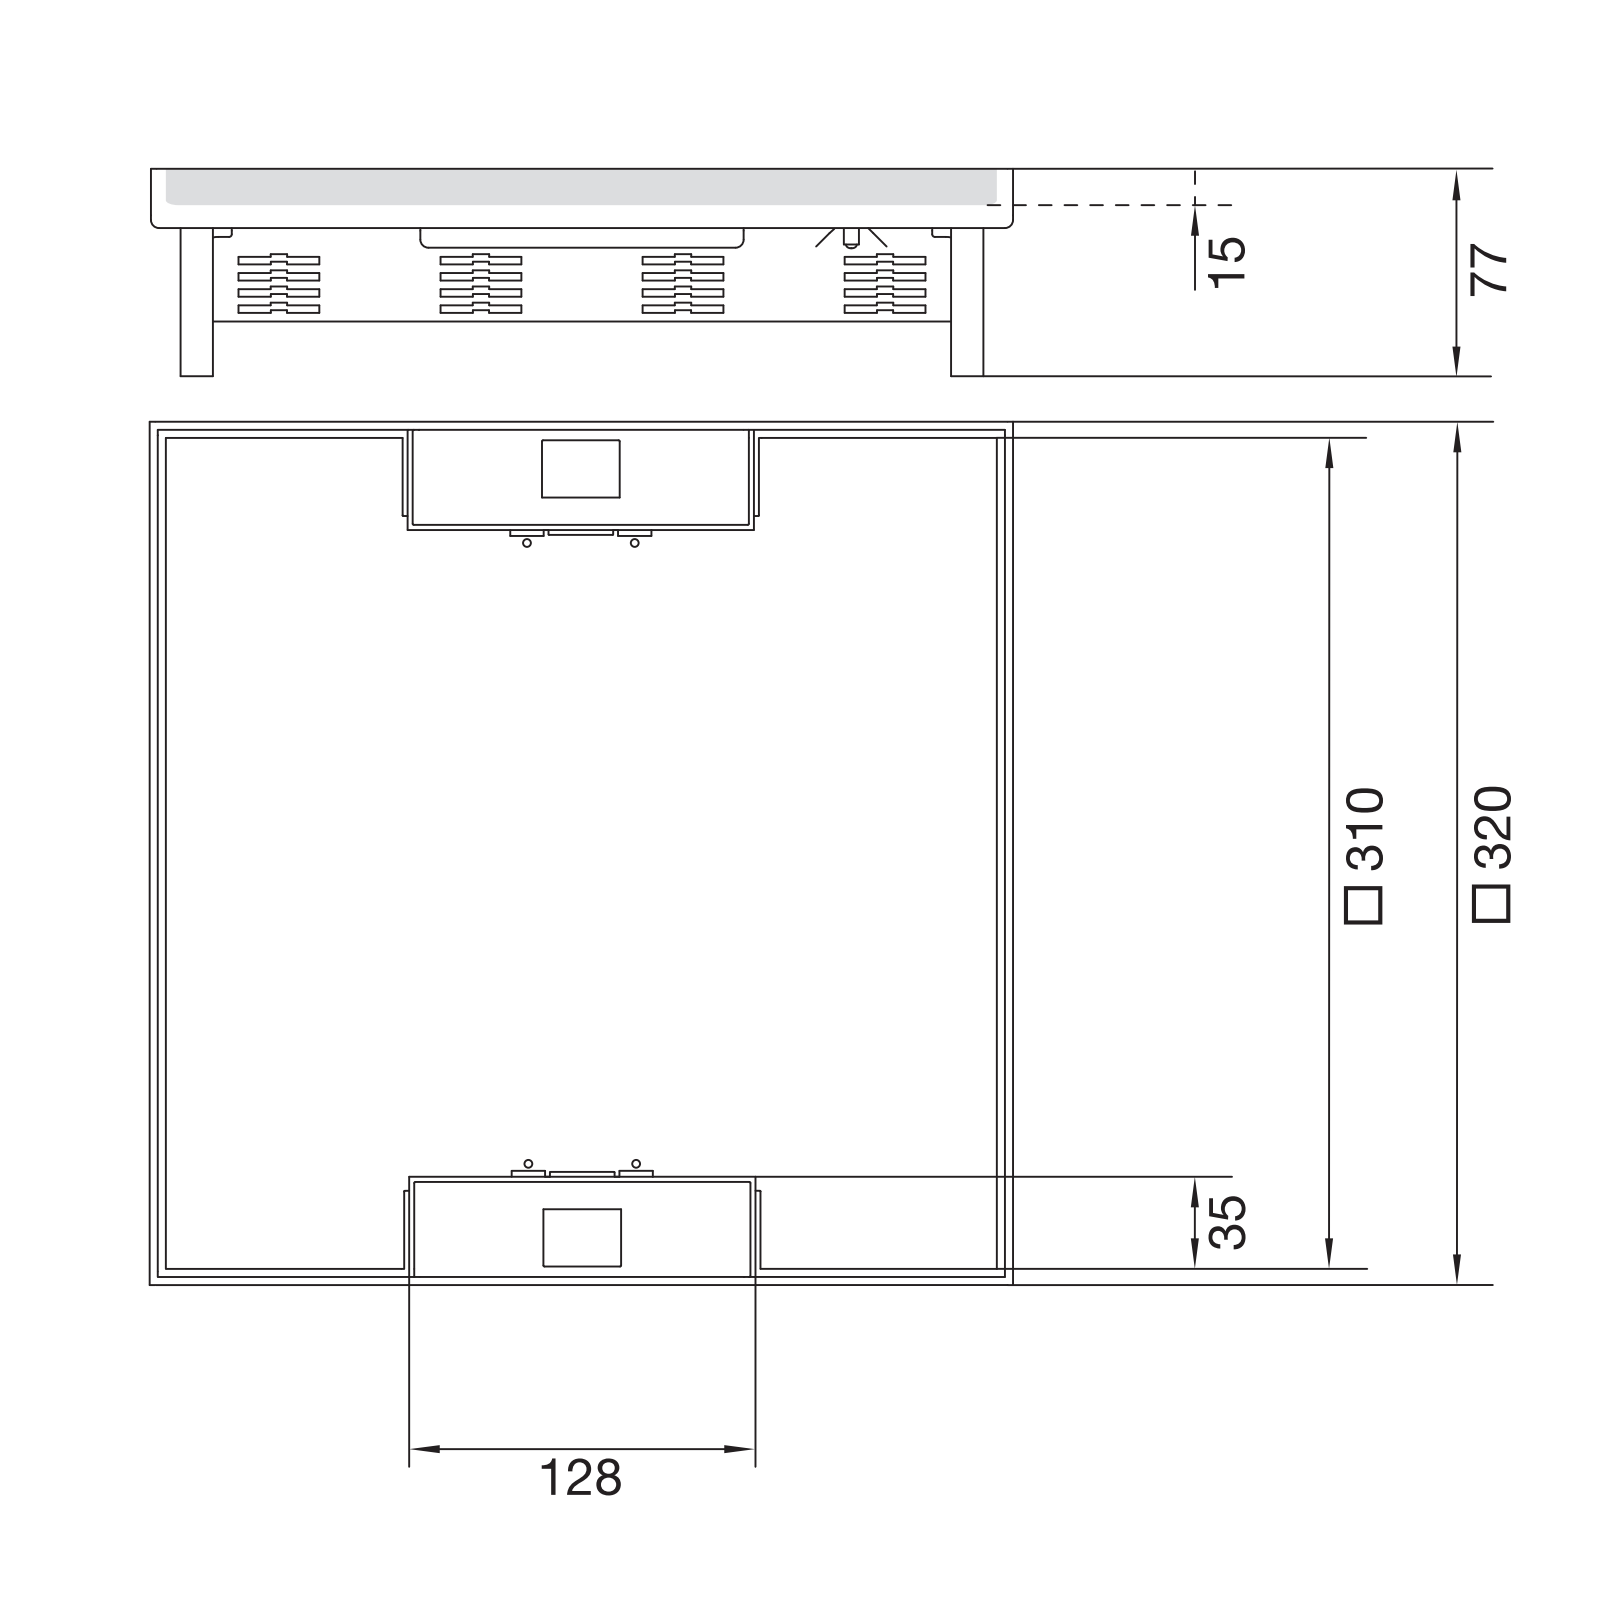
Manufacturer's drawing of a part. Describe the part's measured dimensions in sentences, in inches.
The part is named "T-00644_1; U09001_1; T-00833_ASM_1_ASM; T-00651_1 (+7 more)". Its 3-D file was written by "CREO PARAMETRIC BY PTC INC, 2022281 (AUTOMOTIVE_DESIGN)". It is 8 solids with 334 faces: 268 planar, 66 cylindrical and 0 other. Overall it measures 12.598 by 12.598 by 3.031 inches. Its volume is 23.93 cubic inches and its surface area 633 square inches. Round holes: 4 of diameter 0.106. Round bosses or shafts: 4 of diameter 0.472, 4 of diameter 0.388. Partial cylindrical surfaces (rounded edges, fillets, slot ends): 10 of radius 0.039, 10 of radius 0.118, 6 of radius 0.394, 2 of radius 0.197, 2 of radius 0.26. The main face-to-face distances are 0.079, 0.197, 0.118, 12.402, 0.276, 12.52, 1.783, 10.736, 0.669, 8.953. The hole center spacings are 1.575, 9.055, 9.191.
